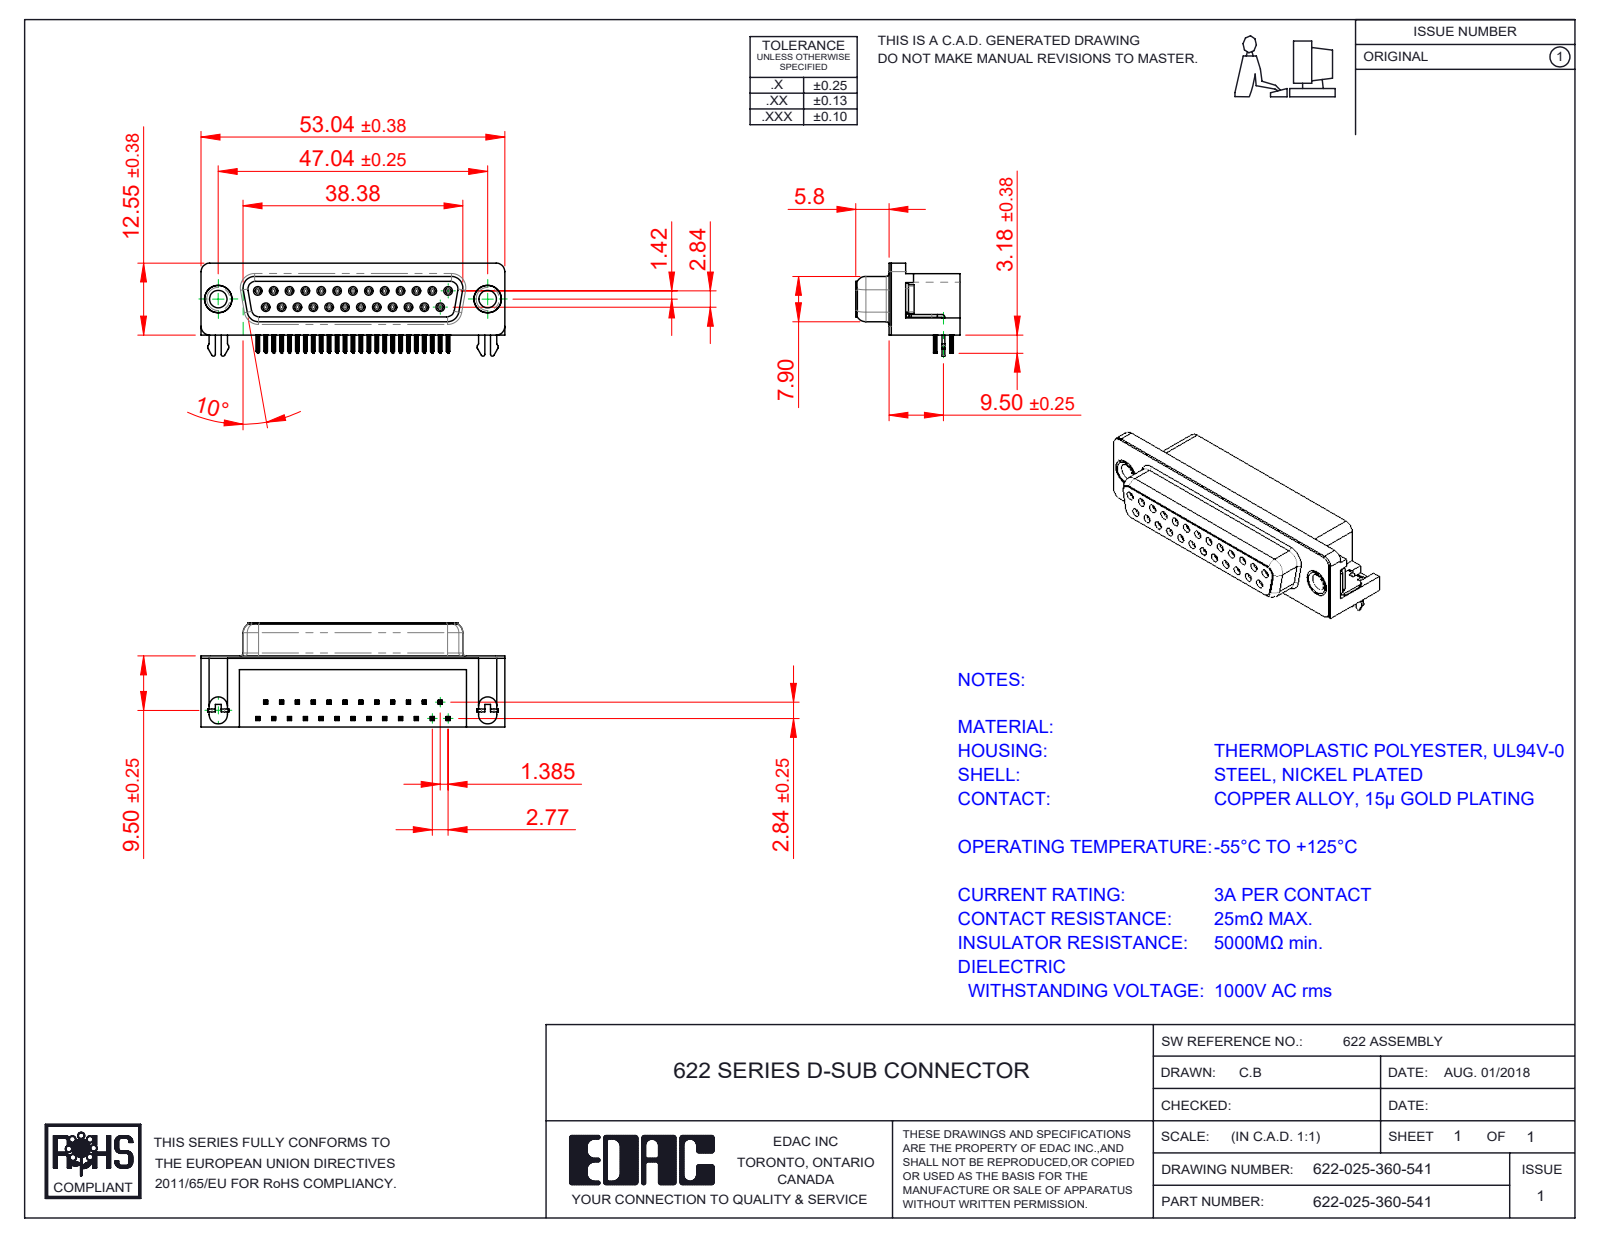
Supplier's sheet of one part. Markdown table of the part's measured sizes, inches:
| quantity | value |
| --- | --- |
| part name | 622 4 Prong Board Lock; 622 Thru Hole Rivet; 622 Shell_25 Socket; 622-025-360-541 (+3 more) |
| STEP written by | SolidWorks 2016 (CONFIG_CONTROL_DESIGN) |
| units | inches |
| bodies | 31 solids, 3932 faces (1766 planar, 908 cylindrical, 1258 other) |
| overall size | 2.088 × 0.717 × 0.64 |
| volume | 0.464 in³ |
| surface area | 14.71 in² |
| round holes (diameter × count) | 0.031 × 25, 0.035 × 25, 0.079 × 2, 0.12 × 2, 0.157 × 2, 0.189 × 2, 0.197 × 2 |
| round bosses / shafts (diameter × count) | 0.047 × 25, 0.193 × 2, 0.187 × 2, 0.152 × 2, 0.118 × 2 |
| partial cylindrical surfaces (radius × count) | 0.004 × 200, 0.006 × 100, 0.014 × 50, 0.013 × 25, 0.039 × 18, 0.01 × 12, 0.011 × 12, 0.053 × 8 |
| main face-to-face distances | 0.016, 0.472, 0.244, 0.407, 0.107, 0.114, 0.125, 0.369, 0.033, 0.262 |
| hole center spacings | 0.124, 0.109, 0.218, 0.327, 0.436, 0.198, 0.198, 0.294 |
